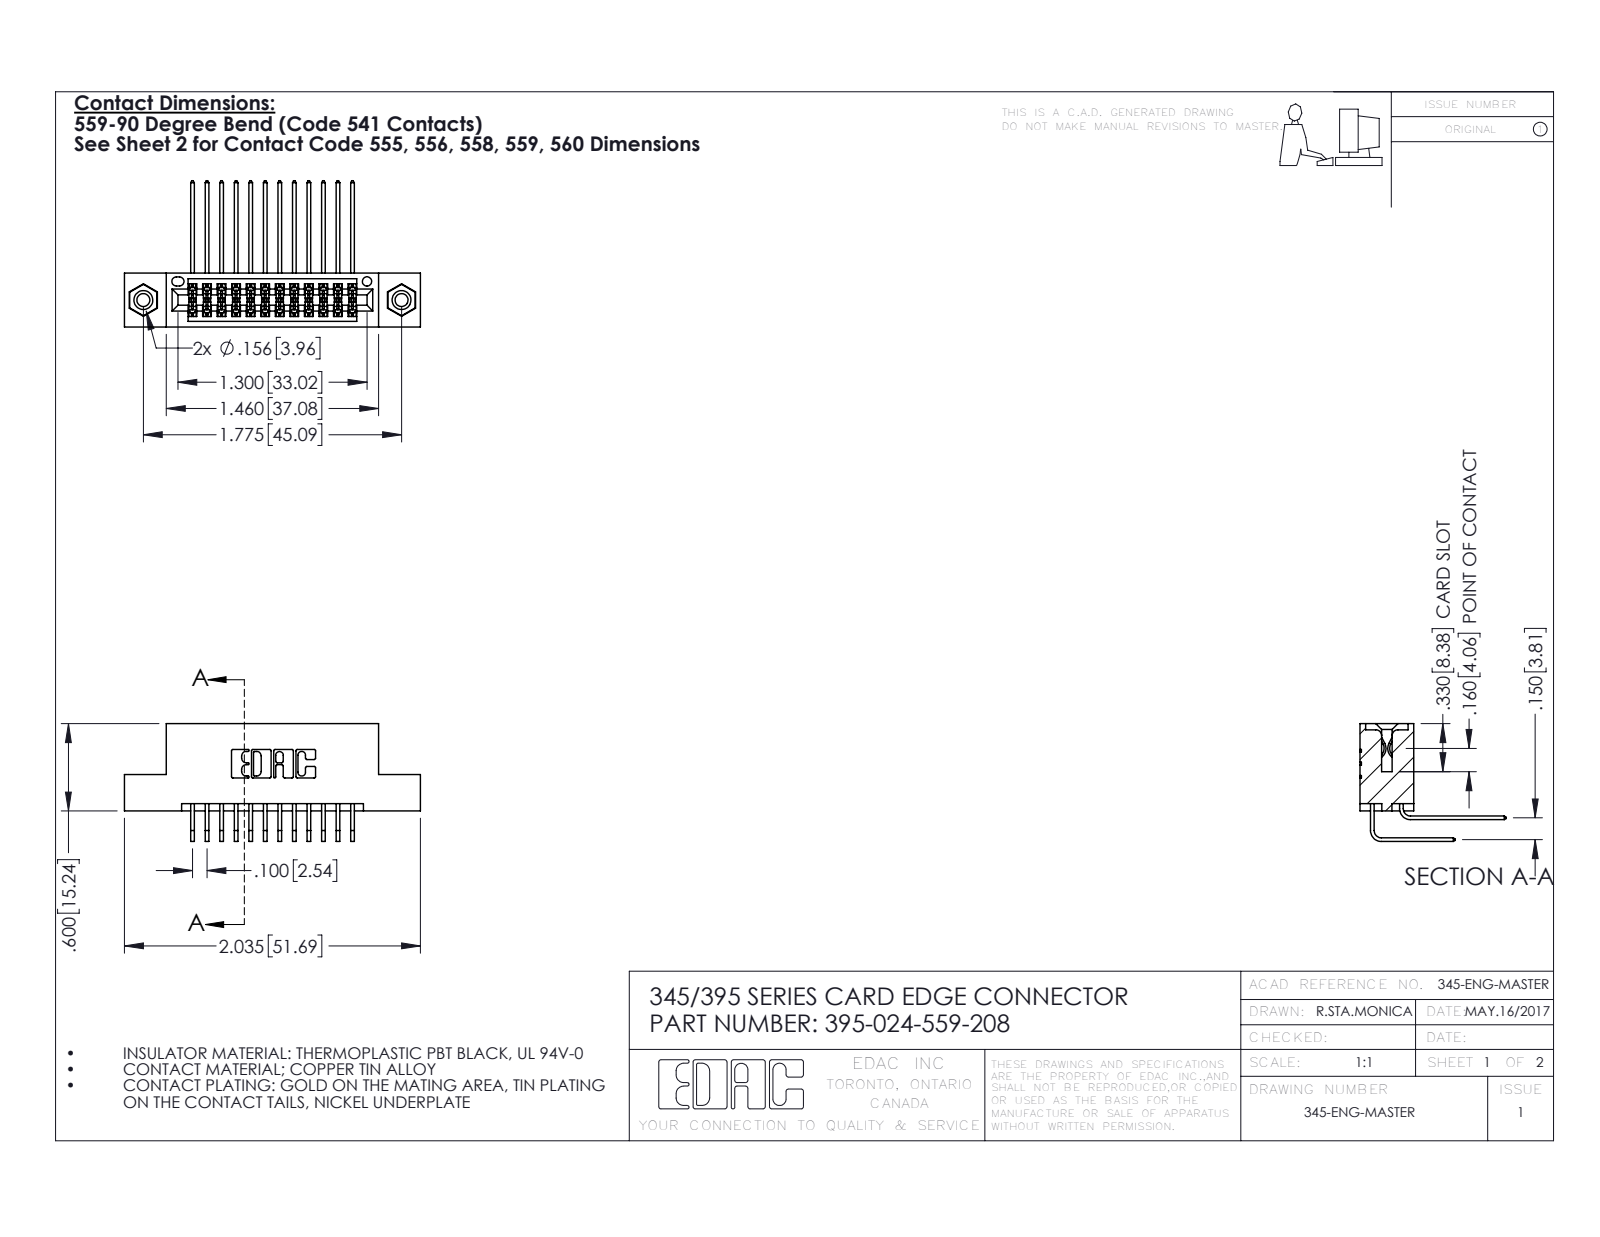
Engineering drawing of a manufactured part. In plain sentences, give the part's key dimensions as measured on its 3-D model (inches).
The part is named "345-250-001_345-250-003-102; 395-024-559-208; 345-292-001_558 559 Tail - 1; 345 Part_Flush Mounting Lugs - 0.156 Dia-TI (+1 more)". Its 3-D file was written by "SolidWorks 2016 (CONFIG_CONTROL_DESIGN)". It is 27 solids with 1434 faces: 952 planar, 466 cylindrical and 16 other. Overall it measures 2.035 by 1.005 by 0.809 inches. Its volume is 0.297 cubic inches and its surface area 11.3 square inches. Round holes: 2 of diameter 0.089, 2 of diameter 0.125, 2 of diameter 0.156, 1 of diameter 0.064. Round bosses or shafts: 2 of diameter 0.155. Partial cylindrical surfaces (rounded edges, fillets, slot ends): 36 of radius 0.006, 22 of radius 0.01, 6 of radius 0.007, 6 of radius 0.031, 3 of radius 0.026, 2 of radius 0.014, 2 of radius 0.019, 2 of radius 0.022. The main face-to-face distances are 0.2, 0.072, 0.298, 0.37, 0.098, 0.272, 0.025, 0.225, 0.15, 0.1. The hole center spacings are 0.27, 1.543, 1.775.
